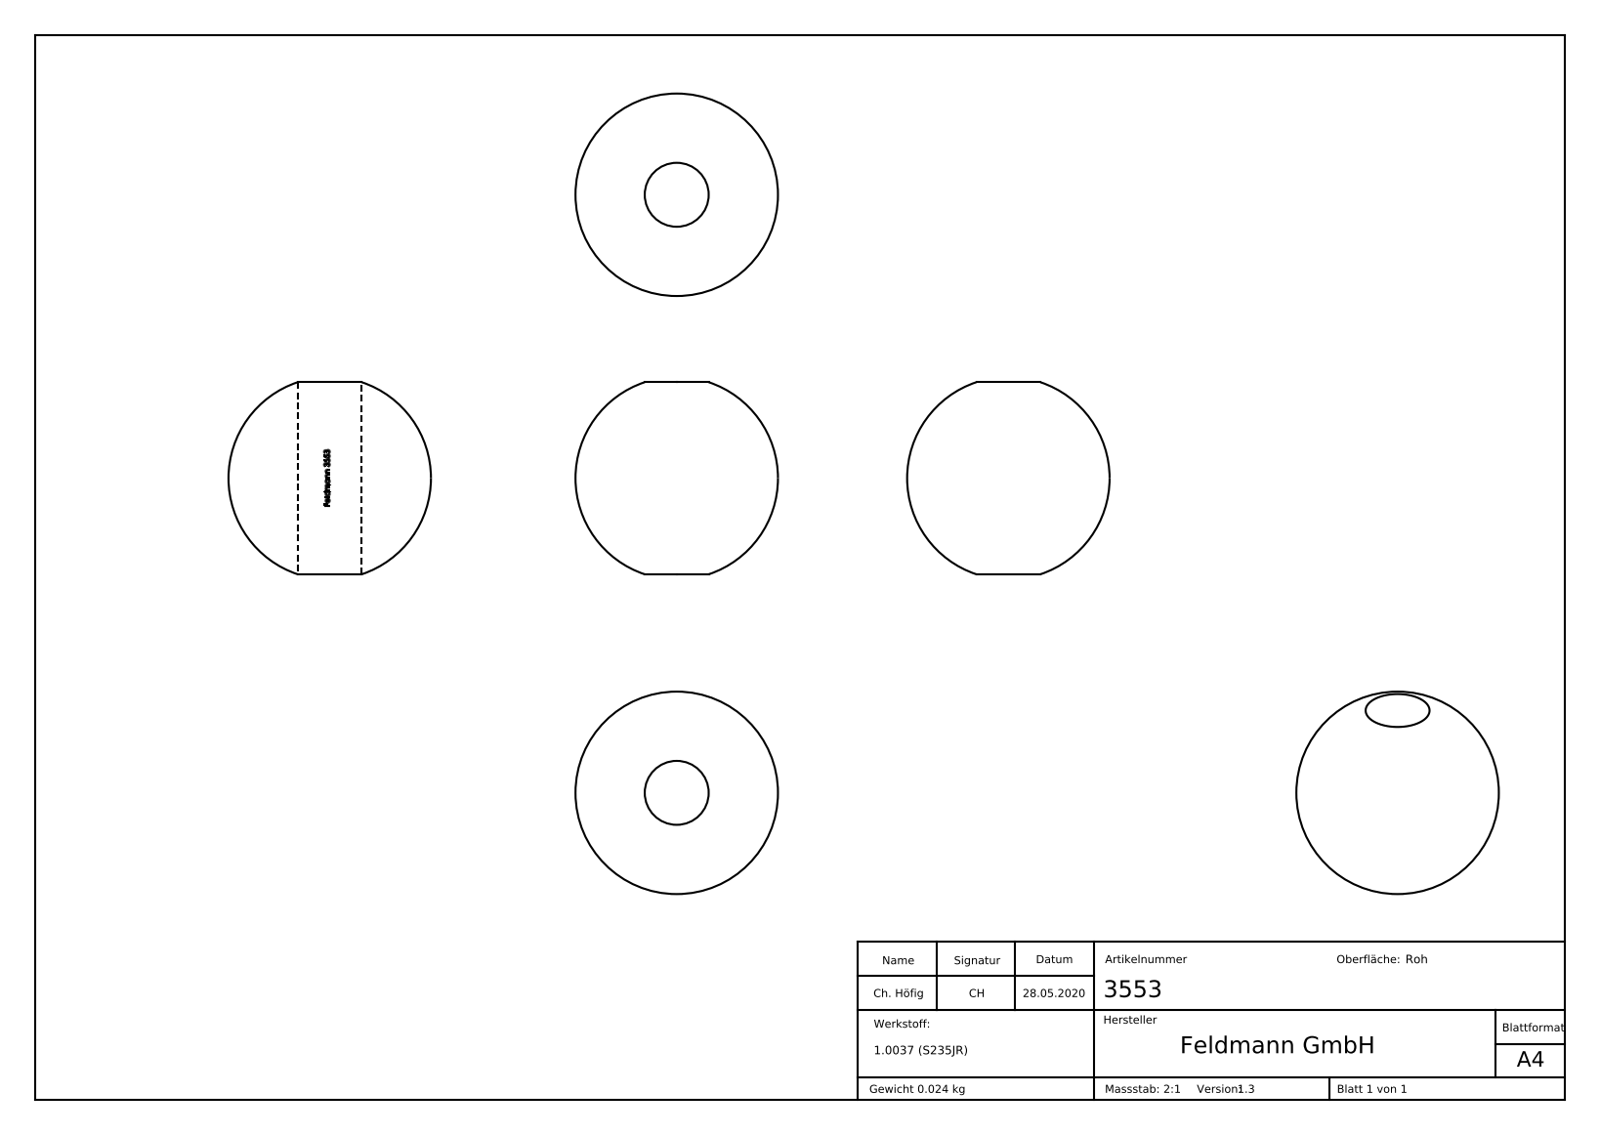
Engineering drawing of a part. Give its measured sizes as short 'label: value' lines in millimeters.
name: 3553
written by: SolidWorks 2015 (CONFIG_CONTROL_DESIGN)
unit: mm
bodies: 1 solid, 181 faces (72 planar, 16 cylindrical, 93 other)
size: 19 × 19 × 18.03
volume: 3 068 mm³; area: 1 419 mm²
holes: 1× ⌀6
rounds: 1× R3.1
face distances: 0.45, 0.55, 0.4, 0.5, 0.81, 0.53, 1.79, 1.84, 1.19, 1.74
